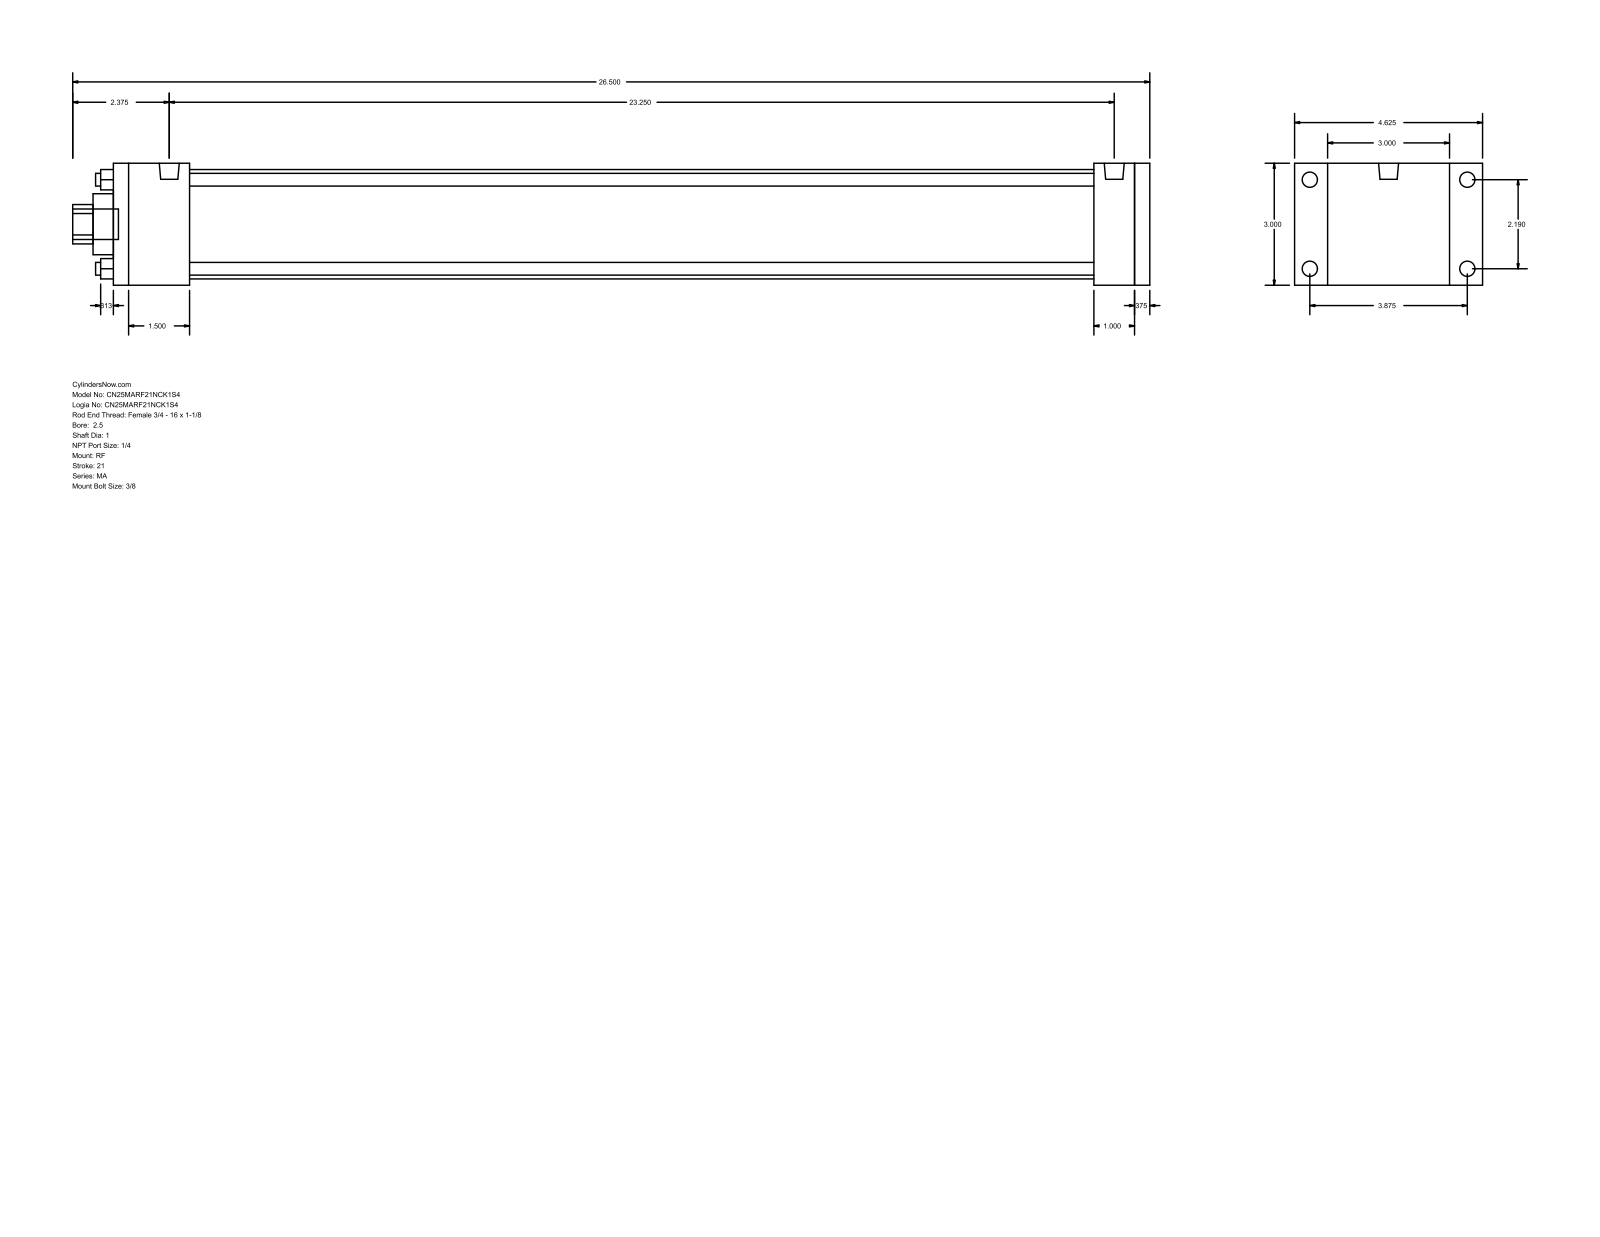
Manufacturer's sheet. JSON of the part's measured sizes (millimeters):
{"part_name": "MA_RF__0250_1", "step_written_by": "GSSL Pune (CONFIG_CONTROL_DESIGN)", "units": "millimeters", "bodies": {"solids": 0, "faces": 92, "planar": 64, "cylindrical": 28, "other": 0}, "overall_size": [673.1, 117.47, 76.2], "round_holes": [[7.94, 4], [25.4, 1], [38.1, 1], [68.33, 1]], "round_bosses_or_shafts": [[9.53, 4], [7.94, 4], [12.49, 2], [19.05, 1]], "partial_cylinders_radius": [[12.29, 1]], "face_to_face_distances": [76.2, 647.7, 638.18, 9.52, 47.63, 612.77, 565.14, 590.55, 600.07, 25.41], "hole_center_spacings": [39.33, 55.62, 78.66]}
